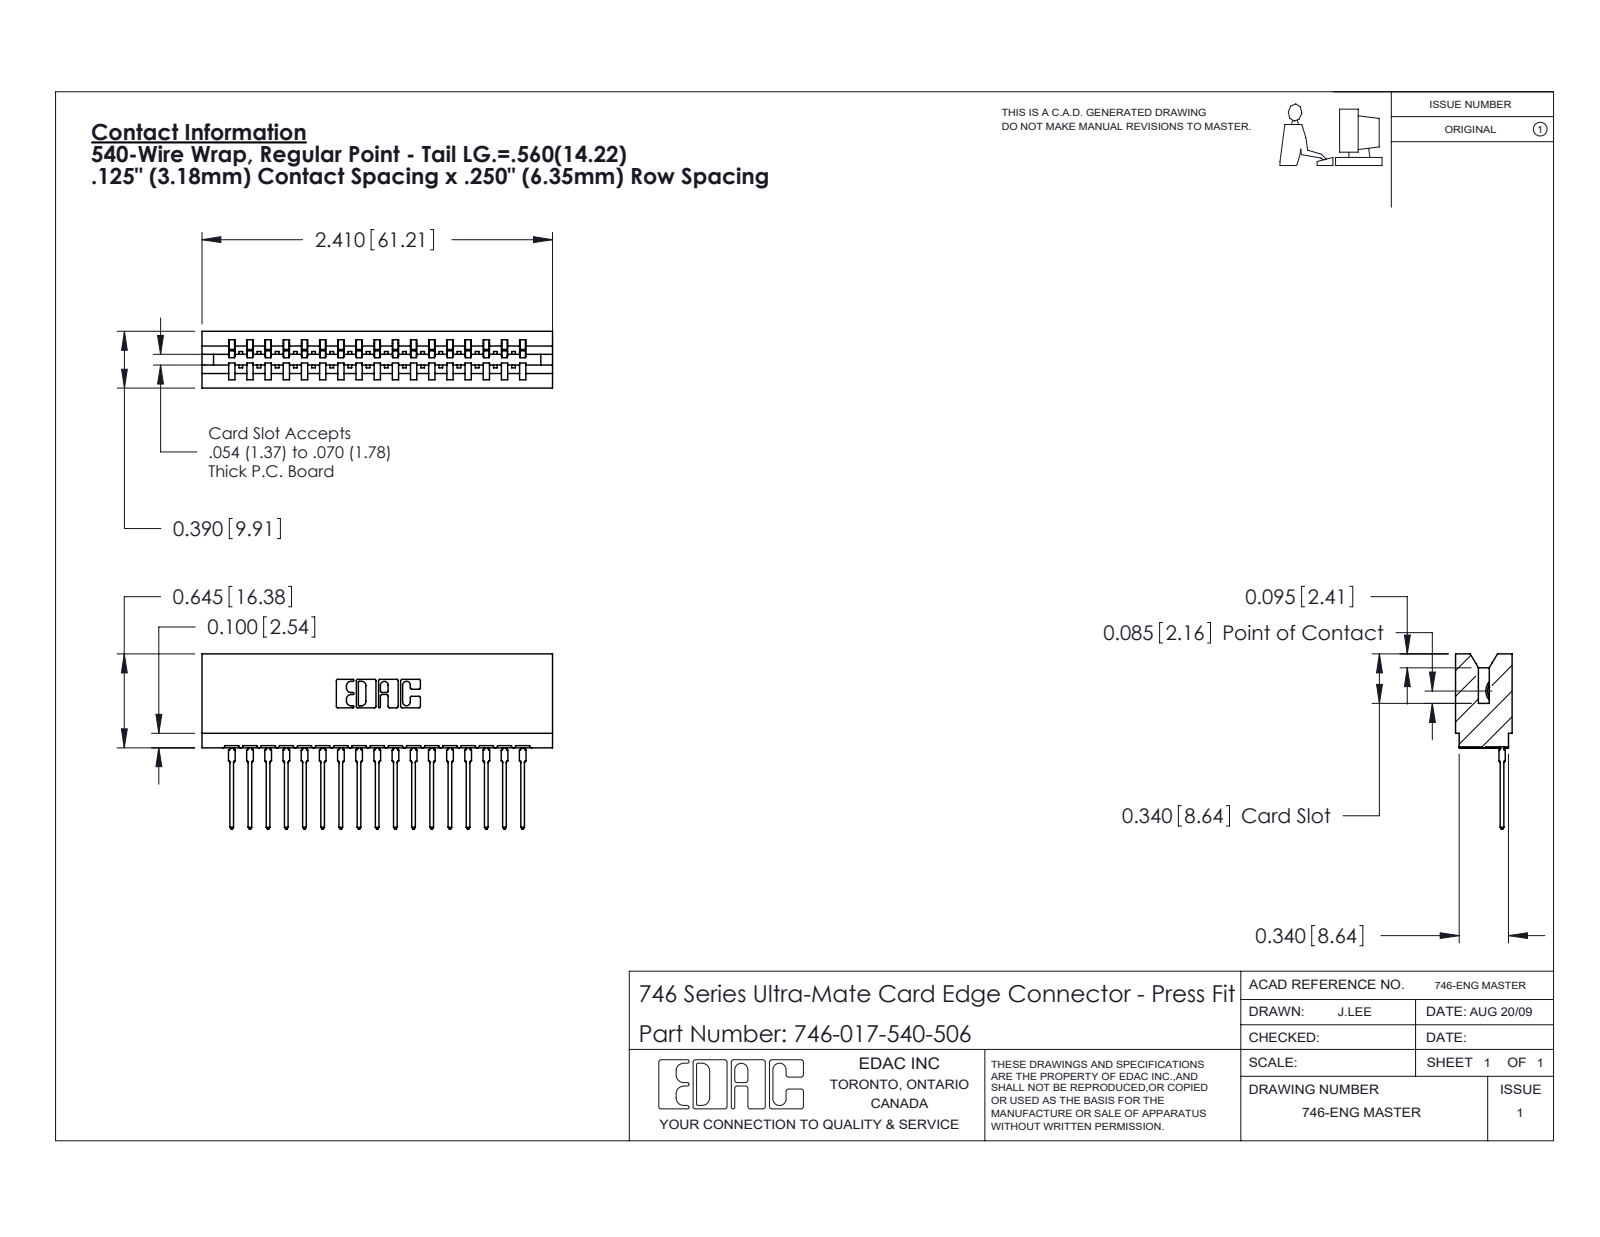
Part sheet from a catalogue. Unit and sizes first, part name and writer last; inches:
Units: inches
Overall size (bounding box): 2.41 × 1.204 × 0.39
Partial cylindrical surfaces — rounded edges, fillets, slot ends (radius × count): R0.021 ×34, R0.01 ×22, R0.015 ×18, R0.007 ×6, R0.031 ×6, R0.005 ×4, R0.011 ×4, R0.026 ×3
Main face-to-face distances: 0.25, 0.057, 0.333, 0.39, 0.5, 0.125, 0.025, 0.307, 0.042, 0.125
Volume: 0.43 in³ · Surface area: 14.47 in²
Bodies: 18 solids, 1934 faces (1127 planar, 365 cylindrical, 442 other)
Part name (STEP PRODUCT): 746-017-540-506; 746-292-001_540; 746 Part_.340 Slot Depth - 06
STEP written by: SolidWorks 2020 (CONFIG_CONTROL_DESIGN)
